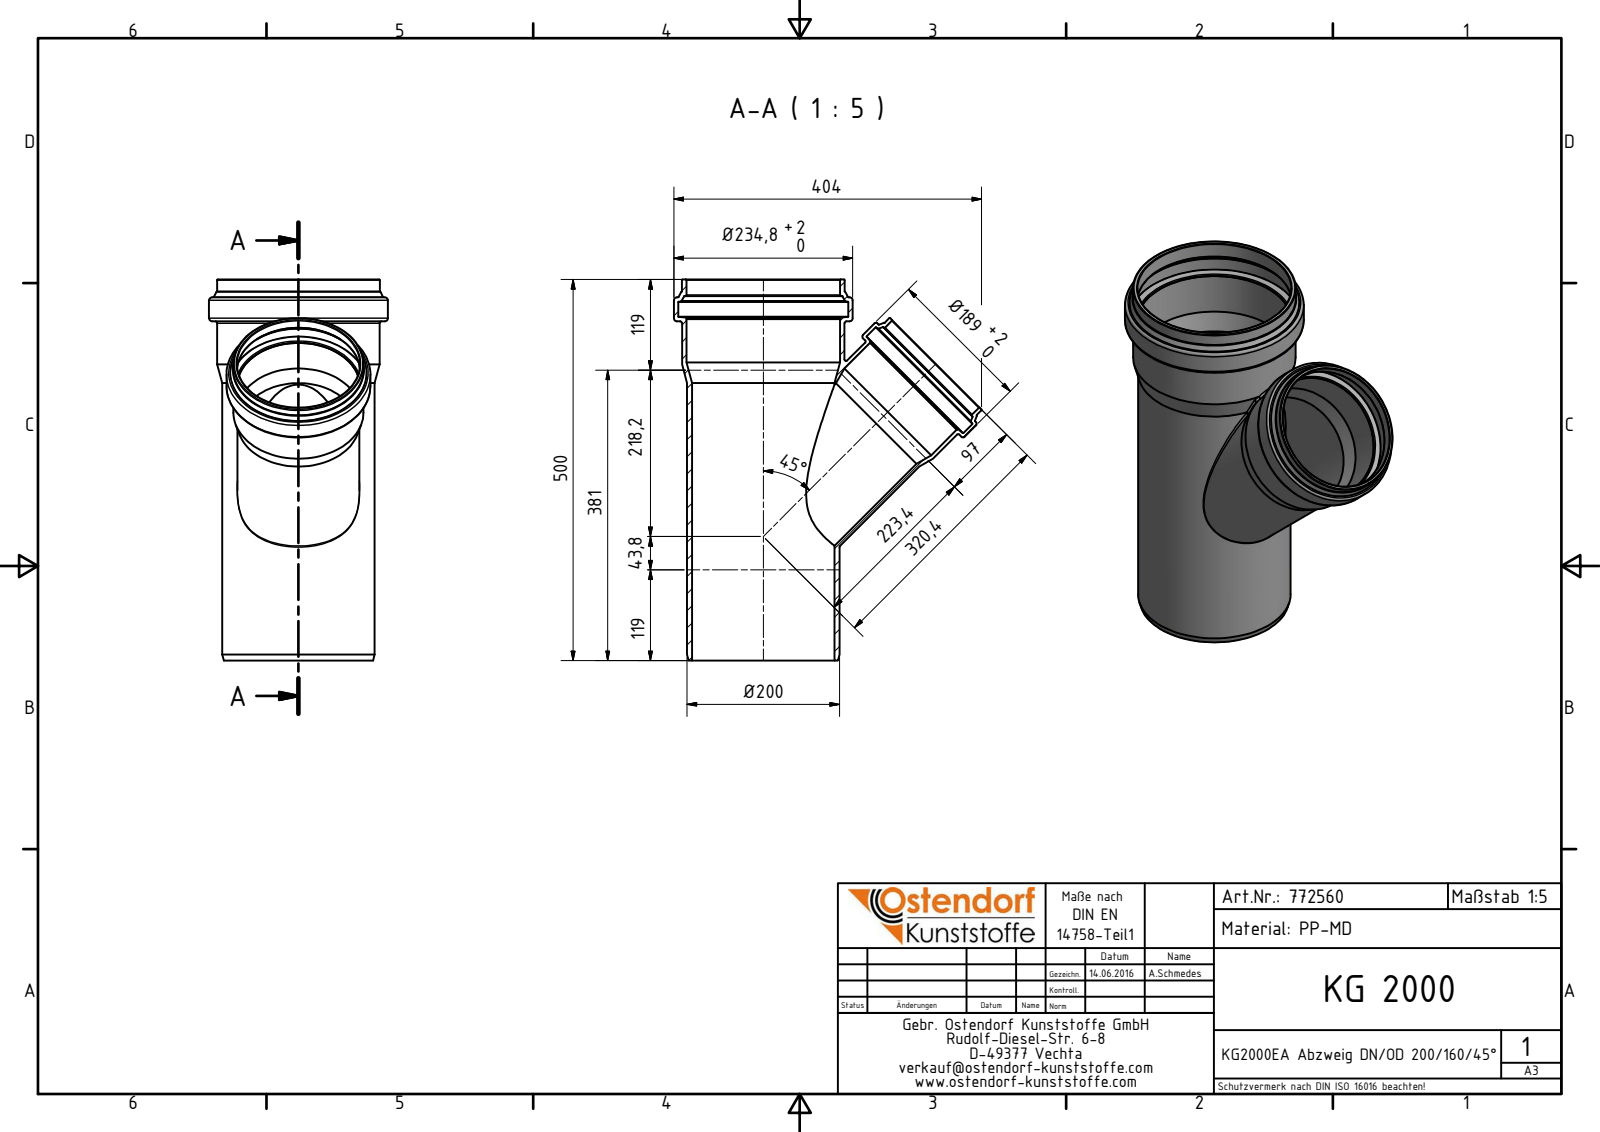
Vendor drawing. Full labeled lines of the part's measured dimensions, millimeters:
Part name (STEP PRODUCT): 772560 KG2000EA Abzweig DN_OD 200_160_45°
STEP written by: Autodesk Inventor 2016 (AUTOMOTIVE_DESIGN)
Units: millimetres
Bodies: 1 solid, 78 faces (9 planar, 18 cylindrical, 51 other)
Overall size (bounding box): 500 × 404 × 234.8
Volume: 2 418 000 mm³ · Surface area: 818 197 mm²
Round holes (diameter × count): ⌀161.4 ×2, ⌀149.6 ×1, ⌀161.1 ×1, ⌀179.4 ×1, ⌀187.2 ×1, ⌀201.5 ×1, ⌀201.8 ×1, ⌀223 ×1
Round bosses / shafts (diameter × count): ⌀234.8 ×1, ⌀213.6 ×1, ⌀213.3 ×1, ⌀200.2 ×1, ⌀189 ×1, ⌀171 ×1, ⌀170.7 ×1, ⌀160 ×1
Main face-to-face distances: 445.1, 500, 54.9, 43.99, 476.7, 31.6, 23.3, 27.19, 16.8, 448.13
